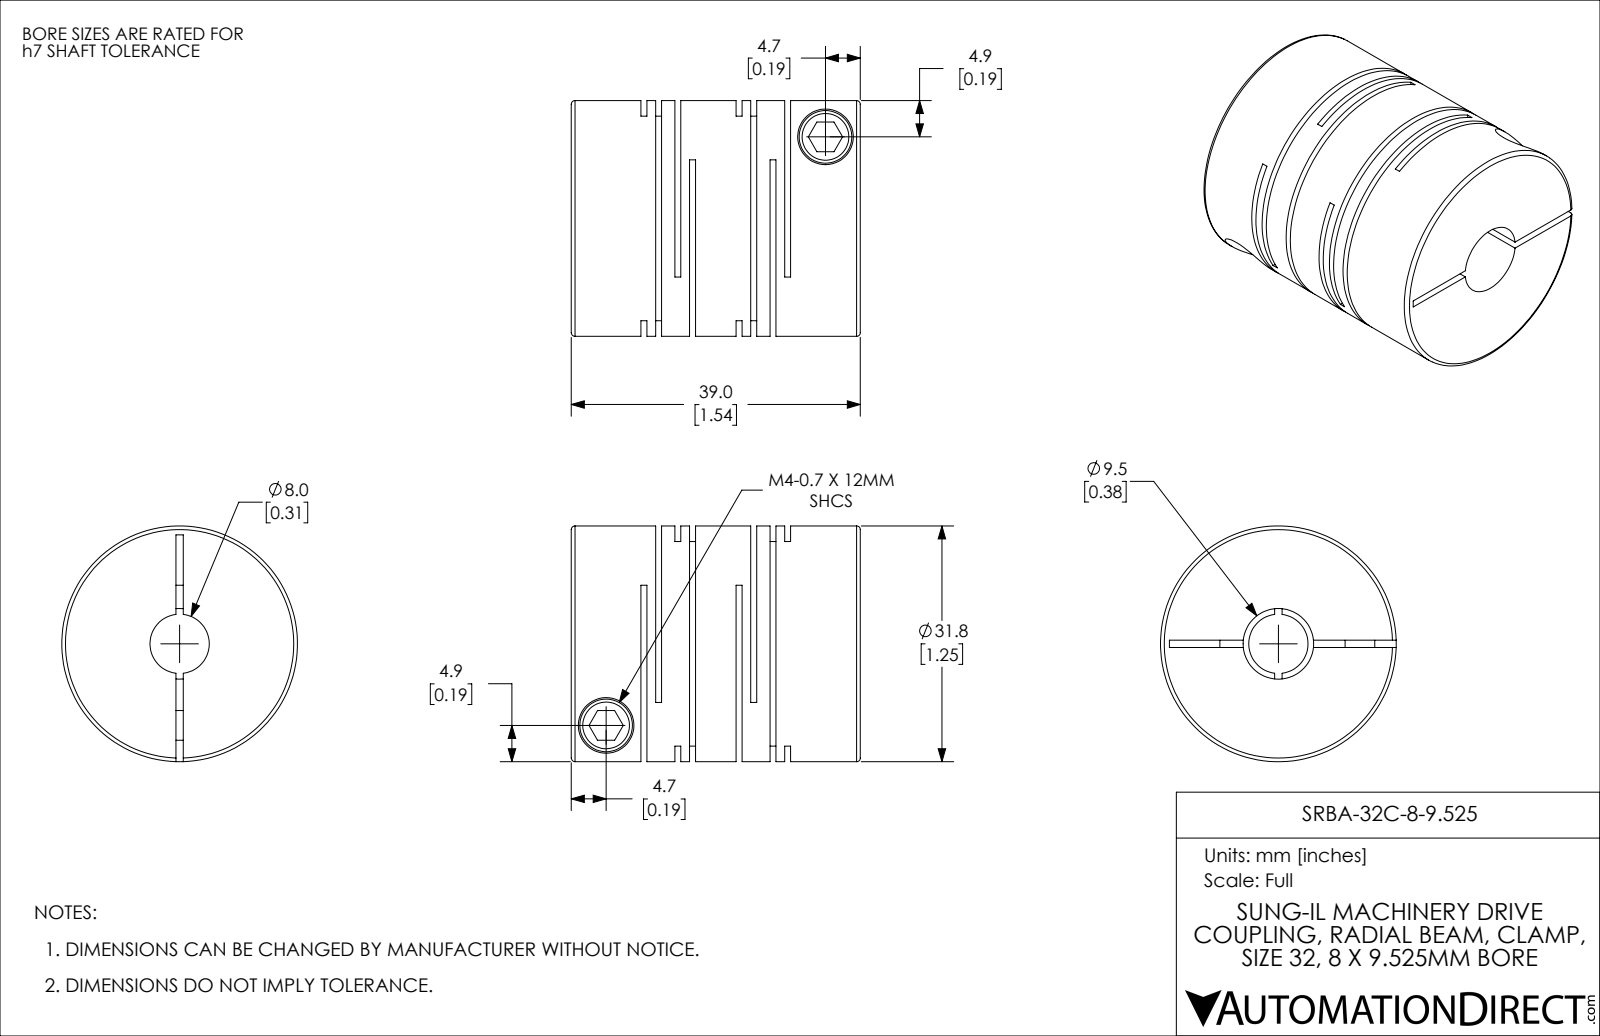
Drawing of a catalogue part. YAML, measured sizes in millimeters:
part_name: "SRBA-32C-8-9.525"
step_written_by: "SolidWorks 2021 (CONFIG_CONTROL_DESIGN)"
units: millimeters
bodies: {solids: 1, faces: 114, planar: 60, cylindrical: 42, other: 12}
overall_size: [39, 31.8, 31.8]
volume: 23861
surface_area: 16329
round_holes:
  - {diameter: 4, count: 2}
  - {diameter: 7.5, count: 2}
  - {diameter: 8, count: 1}
  - {diameter: 9.53, count: 1}
round_bosses_or_shafts:
  - {diameter: 7.1, count: 2}
  - {diameter: 31.8, count: 1}
face_to_face_distances: [0.8, 1.98, 4.58, 12.84, 12.04, 1.18, 10.86, 3.78, 8.26, 2.6]
